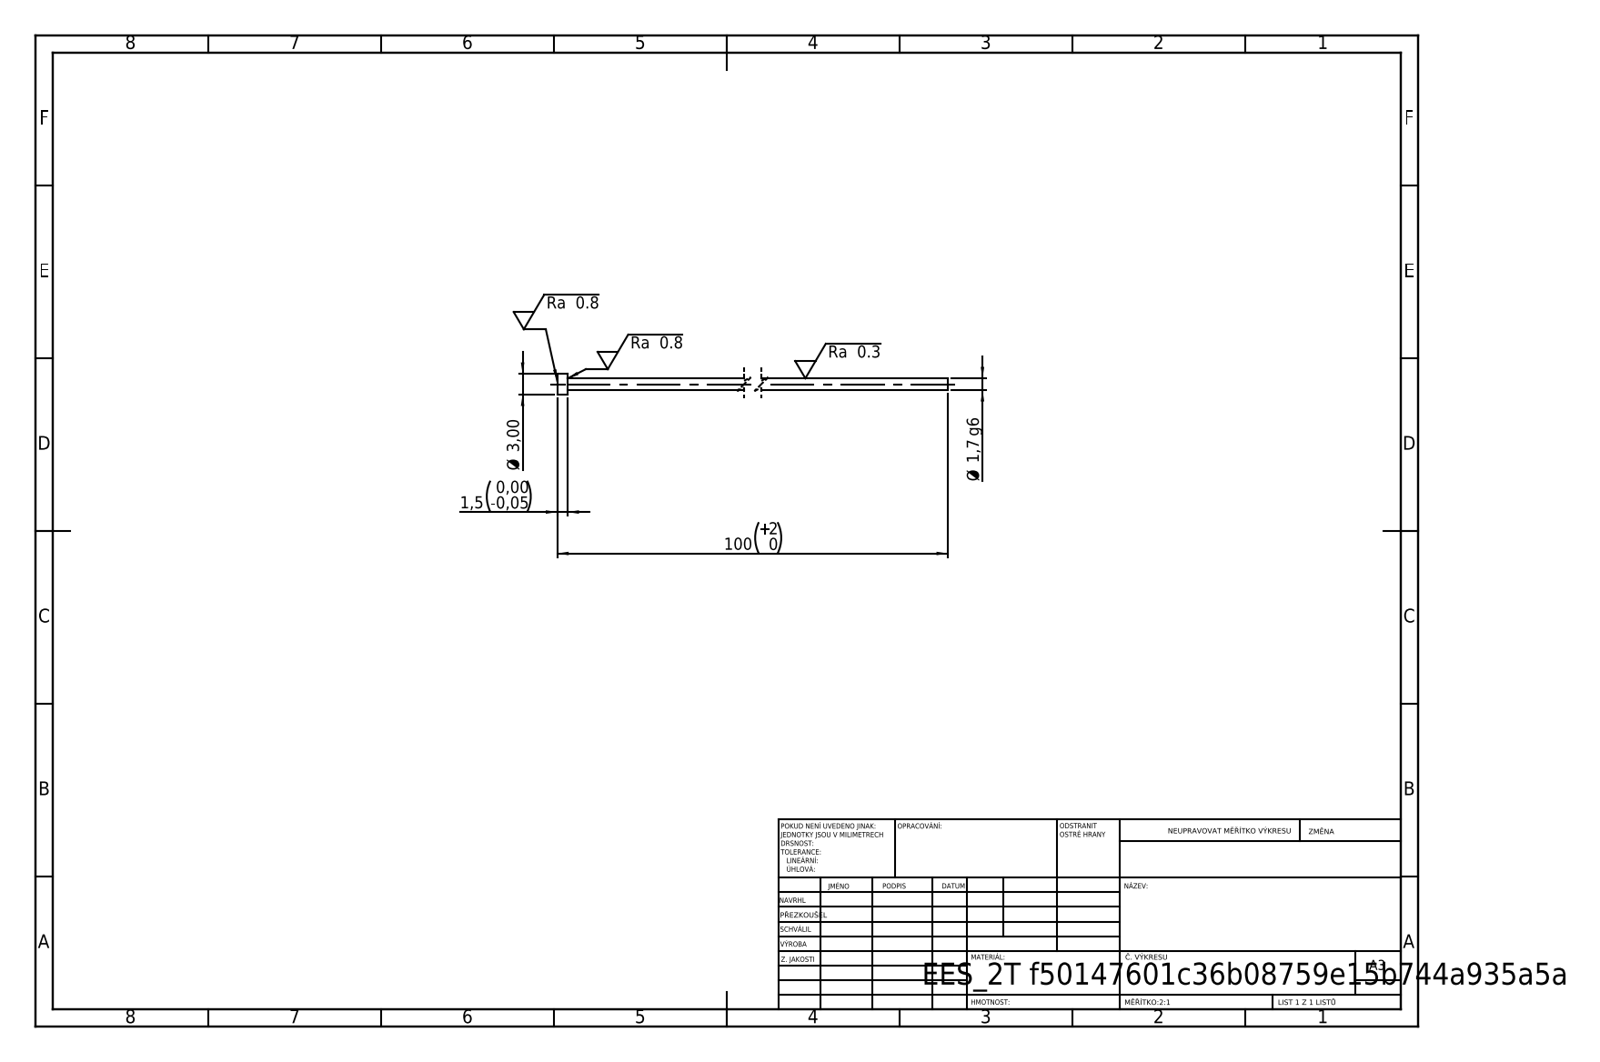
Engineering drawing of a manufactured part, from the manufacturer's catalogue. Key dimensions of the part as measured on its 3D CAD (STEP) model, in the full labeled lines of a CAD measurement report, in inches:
STEP written by: SolidWorks 2019 (CONFIG_CONTROL_DESIGN)
Units: inches
Bodies: 1 solid, 7 faces (3 planar, 4 cylindrical, 0 other)
Overall size (bounding box): 3.937 × 0.118 × 0.118
Volume: 0.014 in³ · Surface area: 0.859 in²
Round bosses / shafts (diameter × count): ⌀0.118 ×1, ⌀0.067 ×1
Main face-to-face distances: 0.059, 3.937, 3.878
